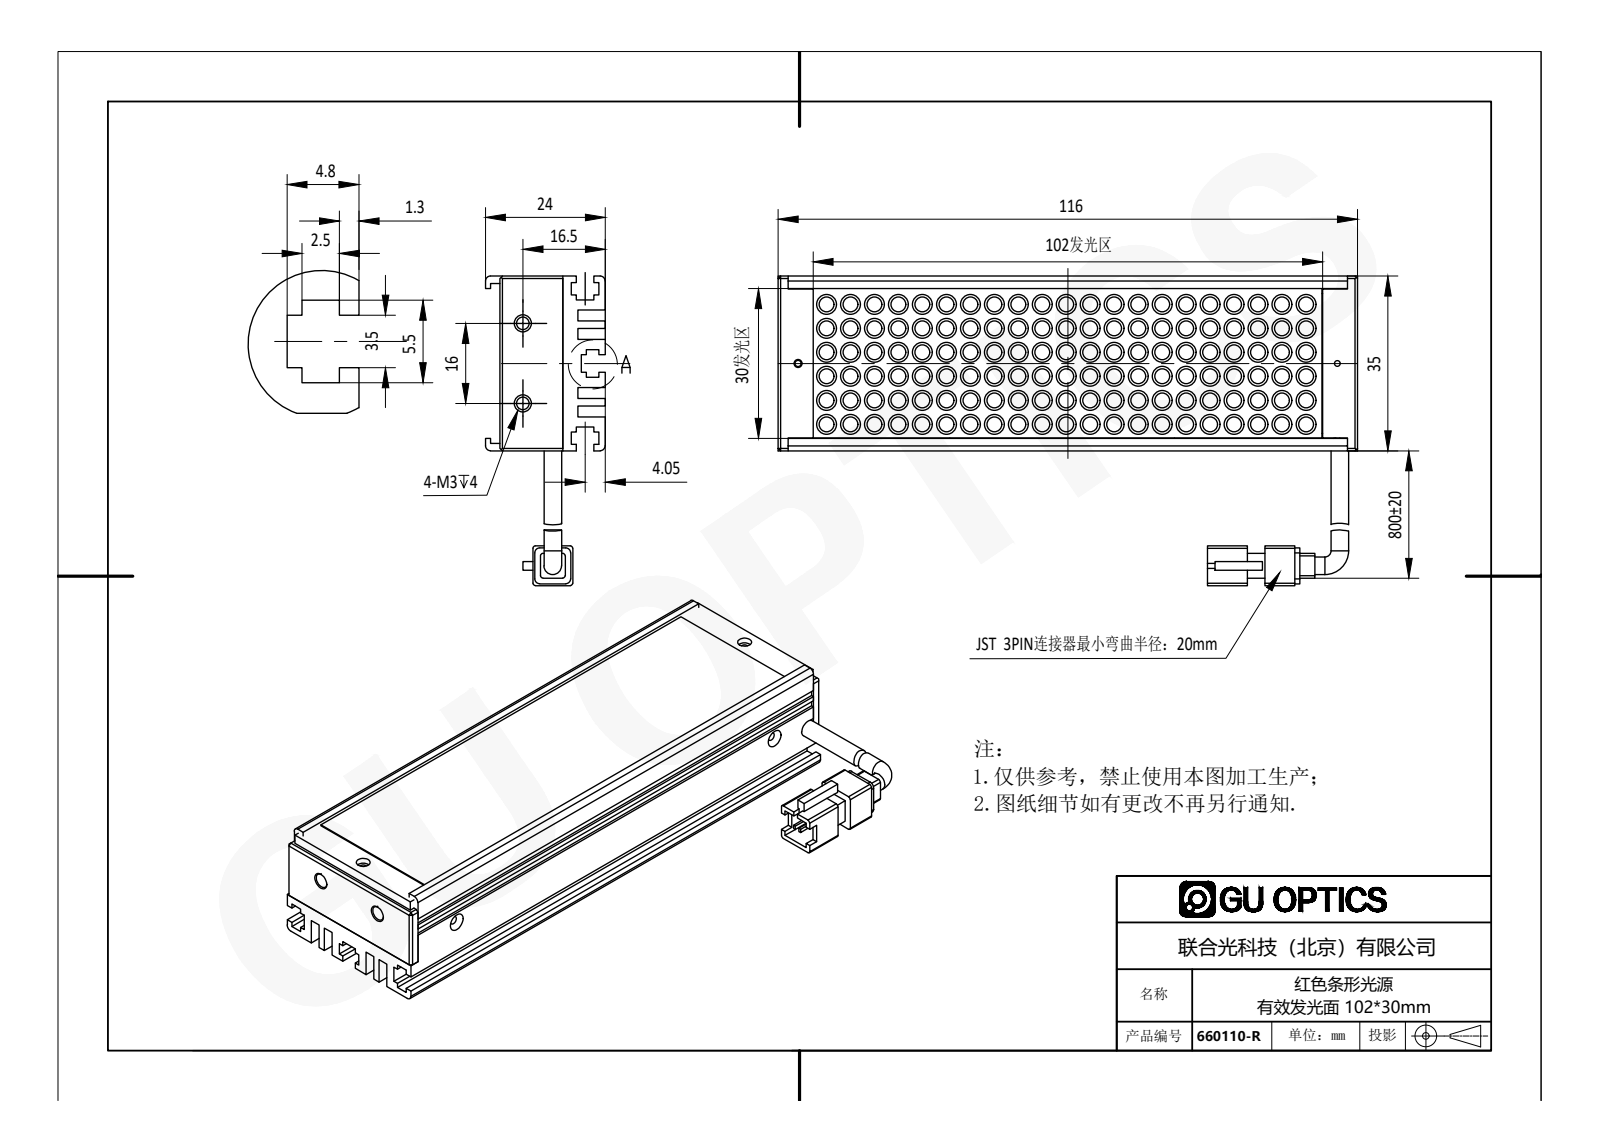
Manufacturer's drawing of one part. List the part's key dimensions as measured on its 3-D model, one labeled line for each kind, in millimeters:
Part name (STEP PRODUCT): 660110-R
STEP written by: SolidWorks 2016 (AUTOMOTIVE_DESIGN)
Units: millimetres
Bodies: 8 solids, 1209 faces (393 planar, 587 cylindrical, 229 other)
Overall size (bounding box): 116 × 62 × 24
Volume: 53 726 mm³ · Surface area: 60 118 mm²
Round holes (diameter × count): ⌀1.6 ×5, ⌀1.5 ×2, ⌀1.7 ×2, ⌀2.5 ×2, ⌀2.8 ×2, ⌀3 ×2, ⌀1.1 ×1, ⌀1.25 ×1, ⌀2 ×1
Round bosses / shafts (diameter × count): ⌀4 ×126, ⌀3 ×126, ⌀3.5 ×2
Partial cylindrical surfaces — rounded edges, fillets, slot ends (radius × count): R1 ×12, R0.5 ×8, R1.65 ×1
Main face-to-face distances: 2, 2.2, 8.6, 1, 2.5, 12.6, 14.6, 9, 4, 7
Hole centre spacings: 108, 7, 9.14, 10.5, 99.01, 99.15, 108.23, 16
